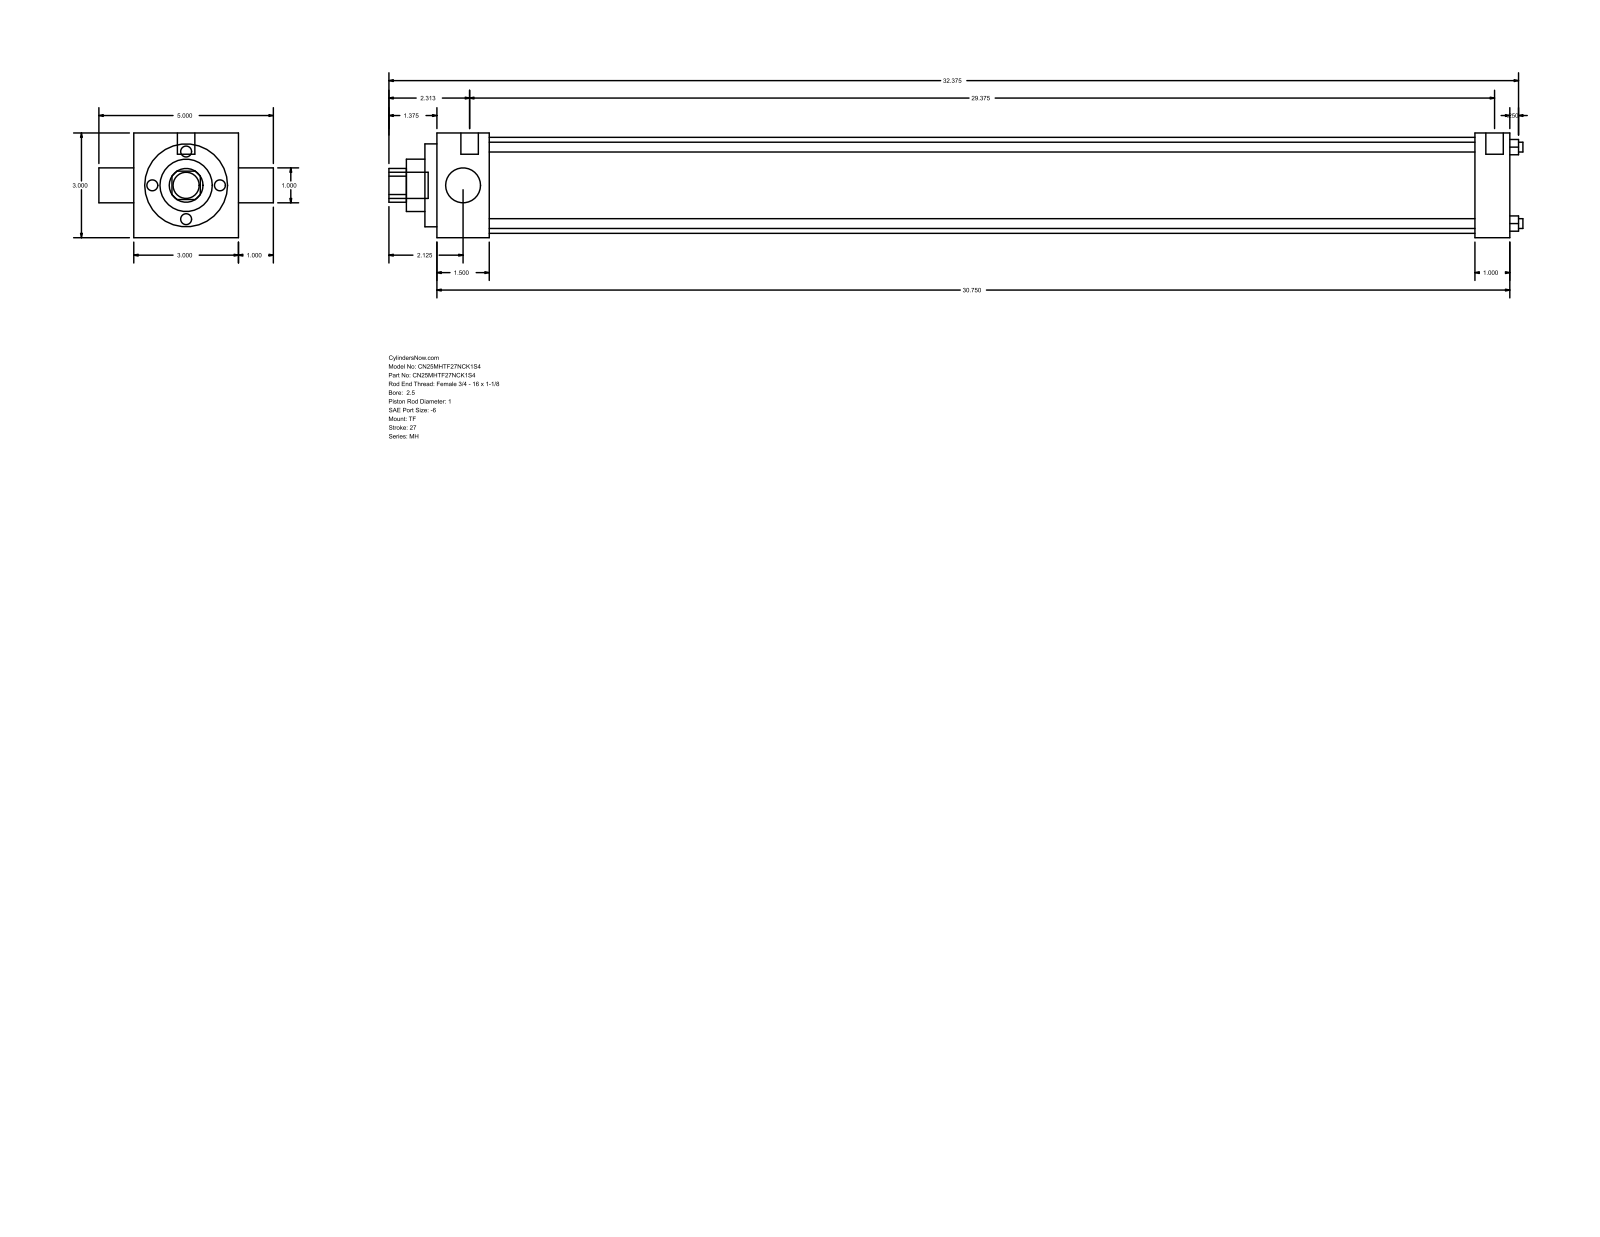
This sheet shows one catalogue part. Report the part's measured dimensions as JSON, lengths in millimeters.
{"part_name": "MH_TF__0250_1", "step_written_by": "GSSL Pune (CONFIG_CONTROL_DESIGN)", "units": "millimeters", "bodies": {"solids": 0, "faces": 86, "planar": 61, "cylindrical": 25, "other": 0}, "overall_size": [825.5, 127, 76.2], "round_holes": [[7.14, 4], [25.4, 2], [38.1, 1], [60.33, 1], [69.85, 1]], "round_bosses_or_shafts": [[5.56, 3], [12.7, 2], [19.05, 1]], "partial_cylinders_radius": [[12.29, 1]], "face_to_face_distances": [76.2, 781.06, 25.4, 38.11, 742.95, 755.66, 717.55, 8.73, 46.84, 764.39], "hole_center_spacings": [39.33, 55.62, 78.66]}
